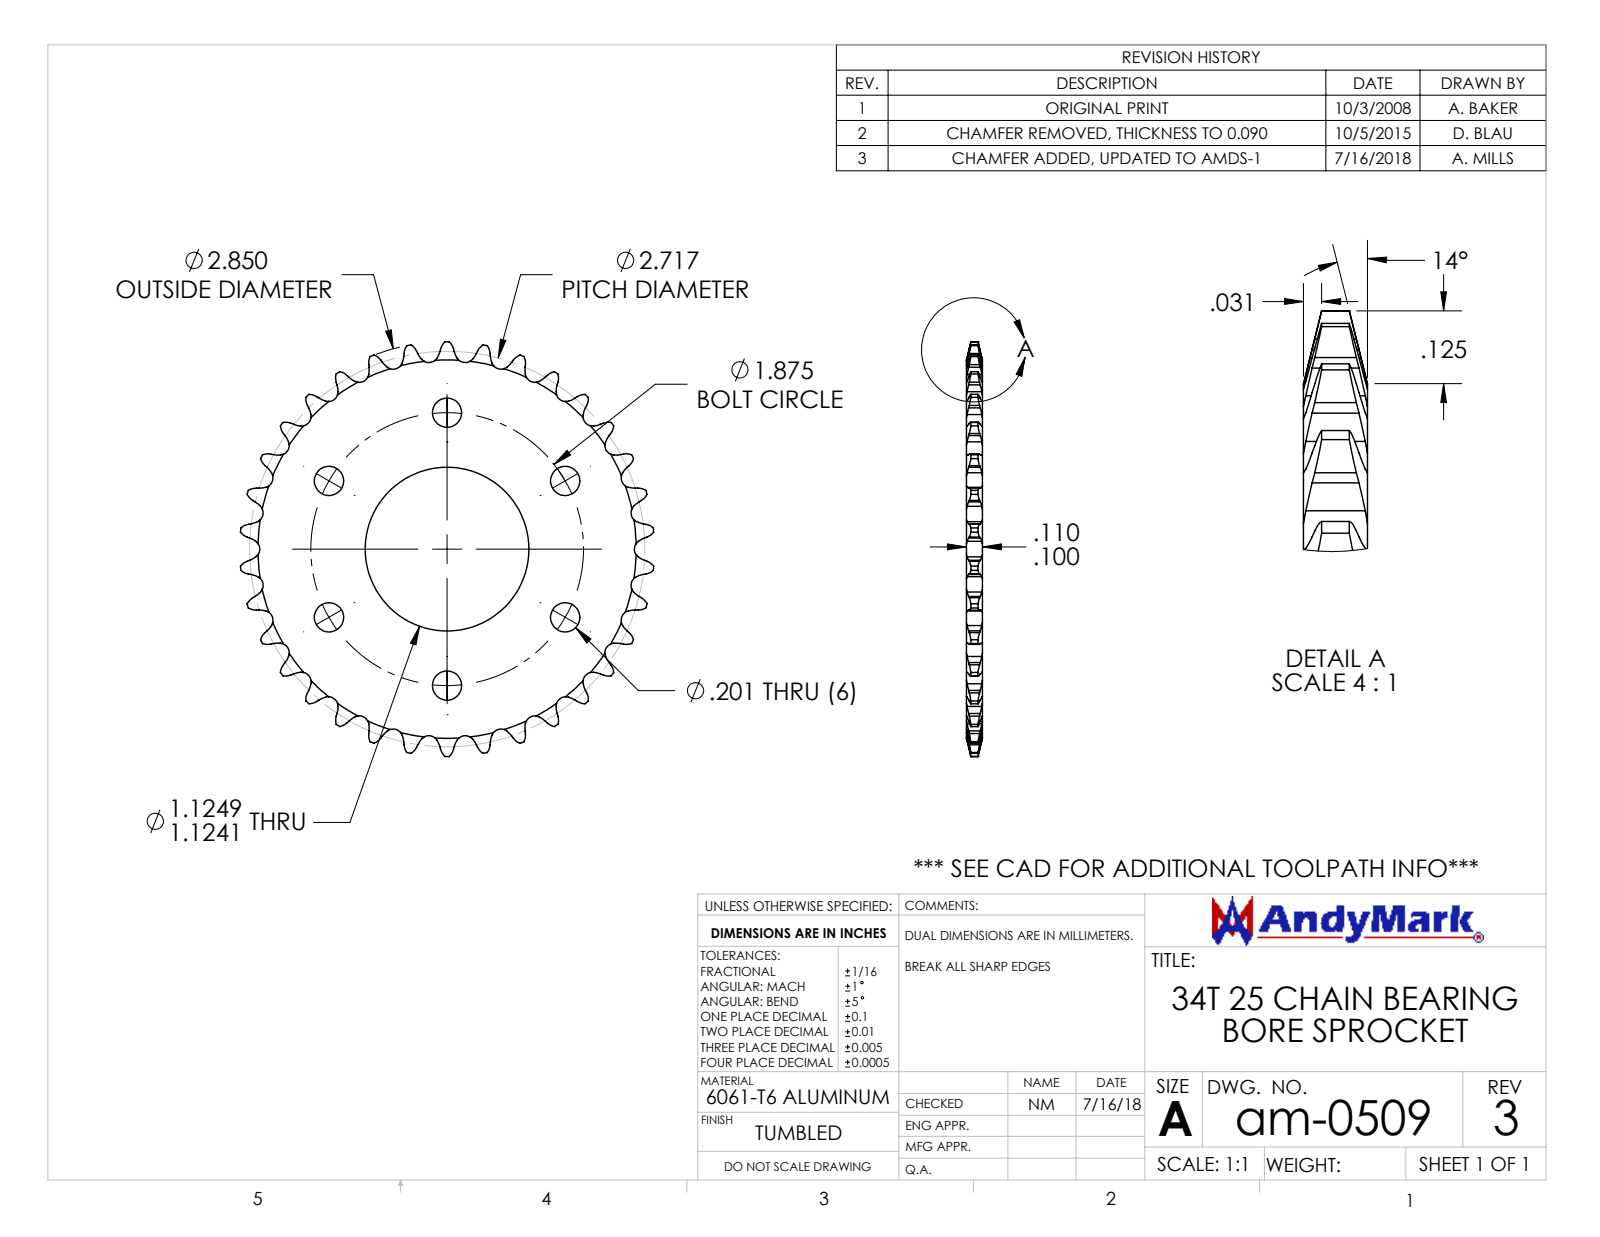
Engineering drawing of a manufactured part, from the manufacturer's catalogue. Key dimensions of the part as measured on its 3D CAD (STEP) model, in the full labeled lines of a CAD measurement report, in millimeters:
Part name (STEP PRODUCT): am-0509_Plate Sprocket
STEP written by: SolidWorks 2018 (AUTOMOTIVE_DESIGN)
Units: millimetres
Bodies: 1 solid, 375 faces (70 planar, 237 cylindrical, 68 other)
Overall size (bounding box): 72.4 × 72.2 × 2.8
Volume: 7 960 mm³ · Surface area: 7 097 mm²
Round holes (diameter × count): ⌀5.1 ×6, ⌀28.6 ×1
Partial cylindrical surfaces — rounded edges, fillets, slot ends (radius × count): R2.7 ×68, R4.3 ×68, R1.7 ×34, R36.2 ×1
Main face-to-face distances: 2.8, 20.4, 20.4, 20.4, 20.4
Hole centre spacings: 23.8, 41.2, 47.6, 23.8
